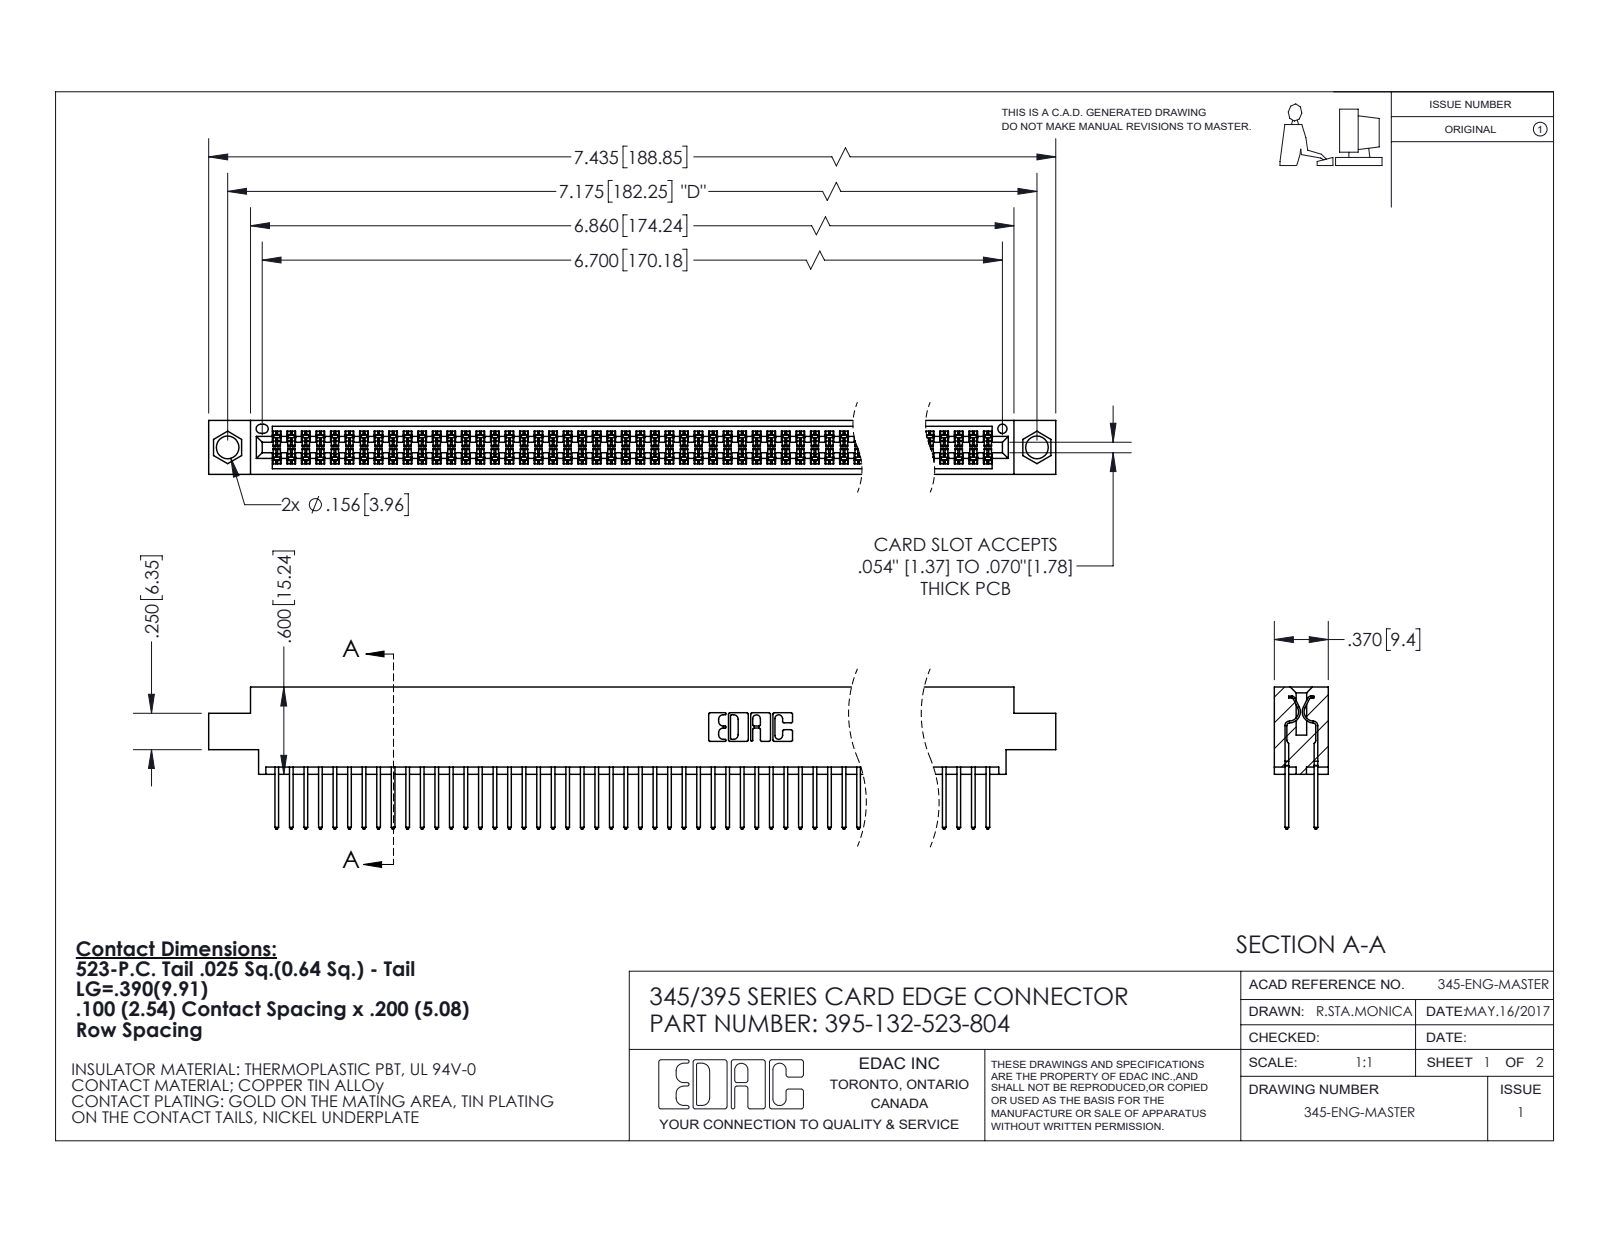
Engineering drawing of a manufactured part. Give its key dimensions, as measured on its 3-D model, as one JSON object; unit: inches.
{"part_name": "345-292-001_345-293-123; 345 Part_0.170 Offset - 0.156 Dia-TI; 395-132-523-804", "step_written_by": "SolidWorks 2020 (CONFIG_CONTROL_DESIGN)", "units": "inches", "bodies": {"solids": 133, "faces": 6744, "planar": 4454, "cylindrical": 2290, "other": 0}, "overall_size": [7.435, 0.977, 0.37], "volume_in3": 1.136, "surface_area_in2": 45.25, "round_holes": [[0.156, 2], [0.064, 1]], "partial_cylinders_radius": [[0.006, 264], [0.01, 132], [0.01, 22], [0.007, 6], [0.031, 6], [0.026, 3], [0.014, 2], [0.019, 2]], "face_to_face_distances": [0.072, 0.298, 0.2, 0.098, 0.272, 0.025, 0.37, 0.225, 0.175, 0.149], "hole_center_spacings": [0.27, 6.939, 7.175]}
